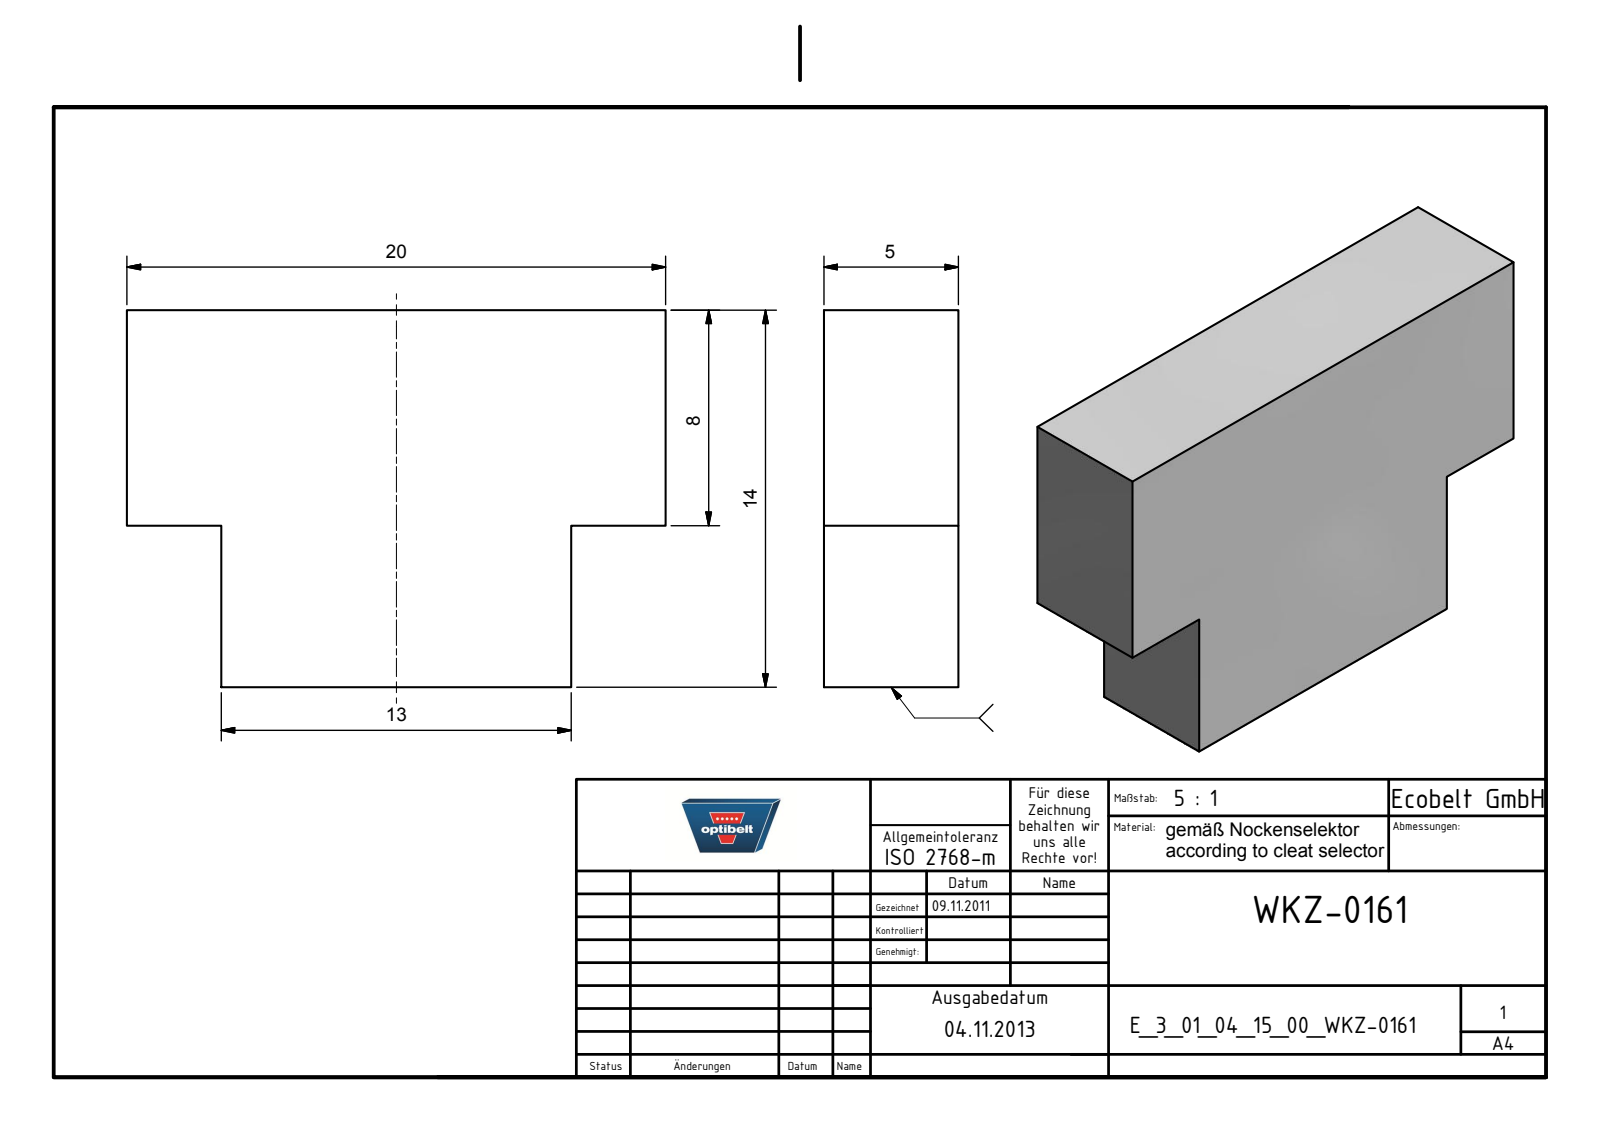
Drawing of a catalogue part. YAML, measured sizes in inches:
part_name: "E_3_01_04_15_00_WKZ-0161"
step_written_by: "Autodesk Inventor 2025 (AUTOMOTIVE_DESIGN)"
units: inches
bodies: {solids: 1, faces: 10, planar: 10, cylindrical: 0, other: 0}
overall_size: [0.787, 0.551, 0.197]
volume: 0.073
surface_area: 1.26
face_to_face_distances: [0.197, 0.551, 0.138, 0.65, 0.787, 0.236, 0.315, 0.512]
